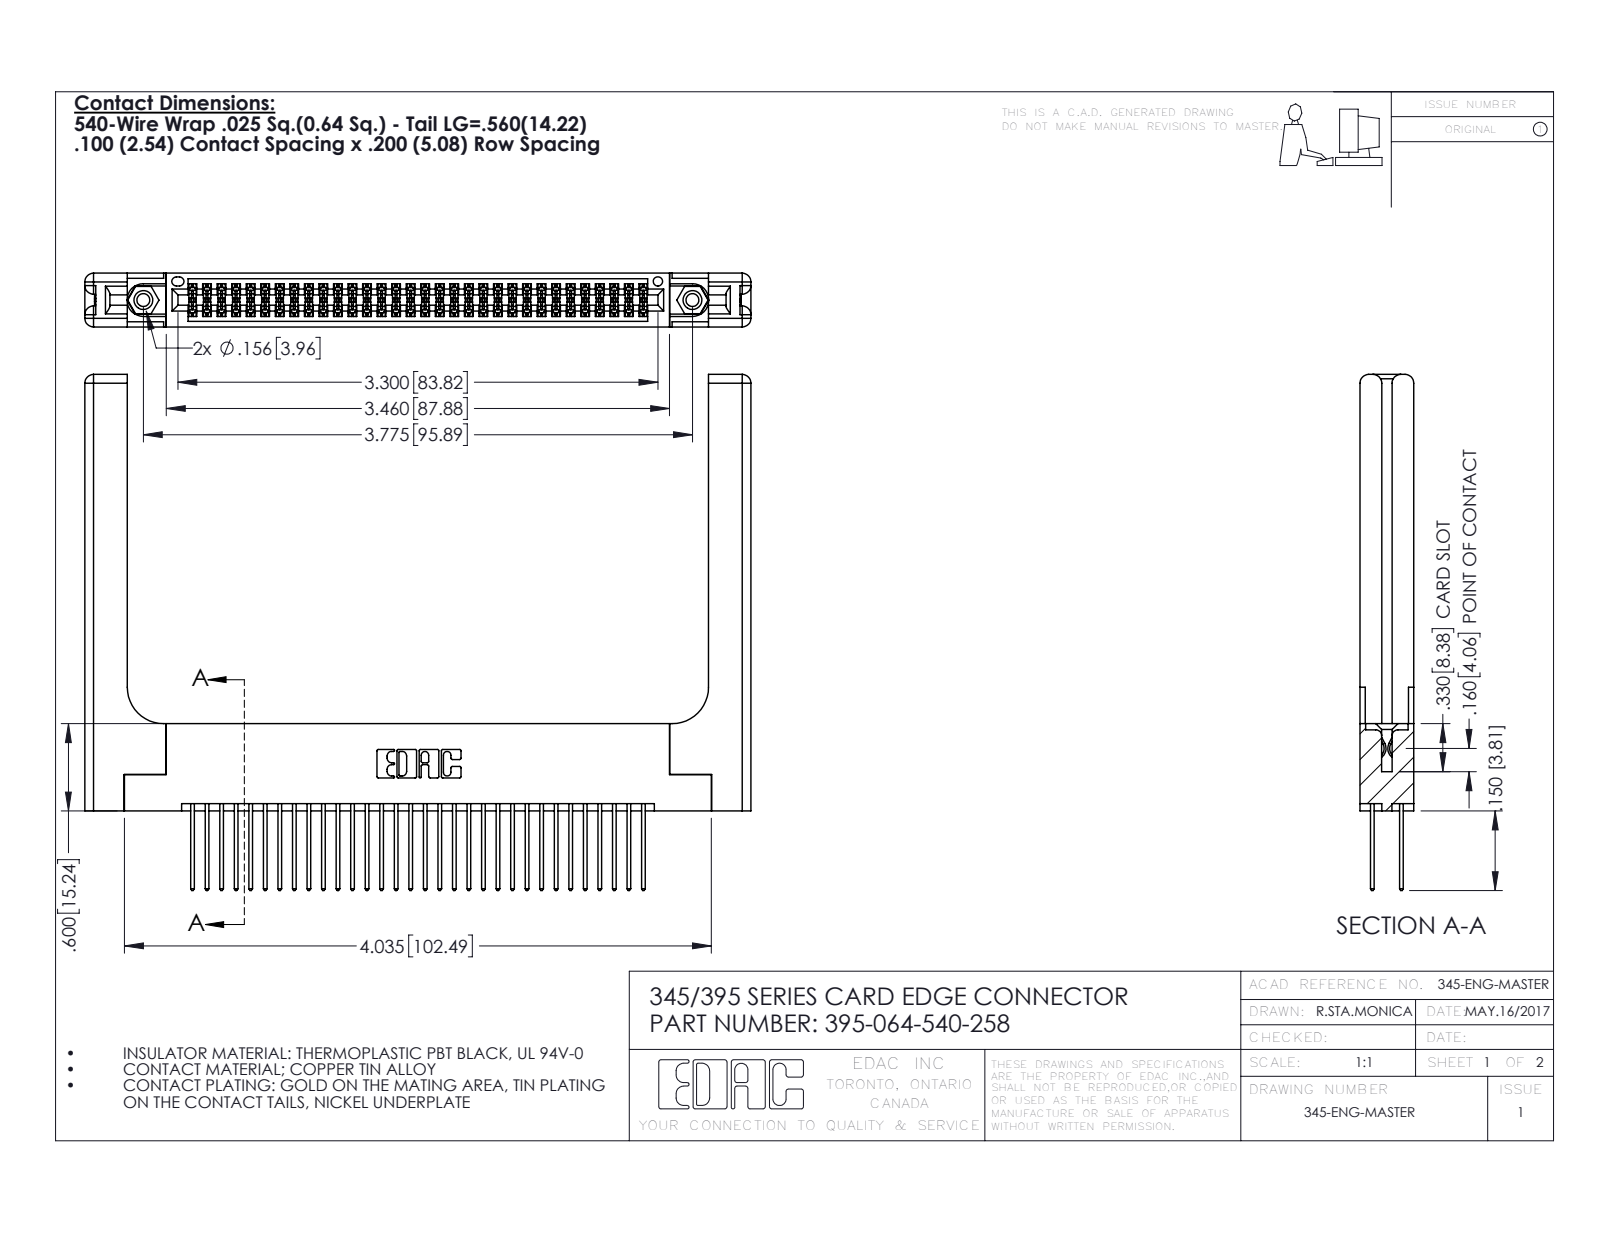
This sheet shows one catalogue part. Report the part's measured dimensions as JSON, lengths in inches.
{"part_name": "345-292-001_345-293-140; 395-064-540-258; 345-220-058_345-220-058; 345-250-001_345-250-001-102 (+1 more)", "step_written_by": "SolidWorks 2016 (CONFIG_CONTROL_DESIGN)", "units": "inches", "bodies": {"solids": 69, "faces": 3582, "planar": 2340, "cylindrical": 1182, "other": 60}, "overall_size": [4.579, 3.547, 0.37], "volume_in3": 1.216, "surface_area_in2": 35.51, "round_holes": [[0.089, 2], [0.125, 2], [0.156, 2], [0.064, 1]], "round_bosses_or_shafts": [[0.155, 2]], "partial_cylinders_radius": [[0.006, 96], [0.01, 64], [0.01, 22], [0.06, 16], [0.007, 6], [0.031, 6], [0.026, 3], [0.014, 2]], "face_to_face_distances": [0.072, 0.298, 0.37, 0.2, 0.098, 0.272, 0.025, 0.225, 0.148, 0.15], "hole_center_spacings": [0.27, 3.54, 3.775]}
